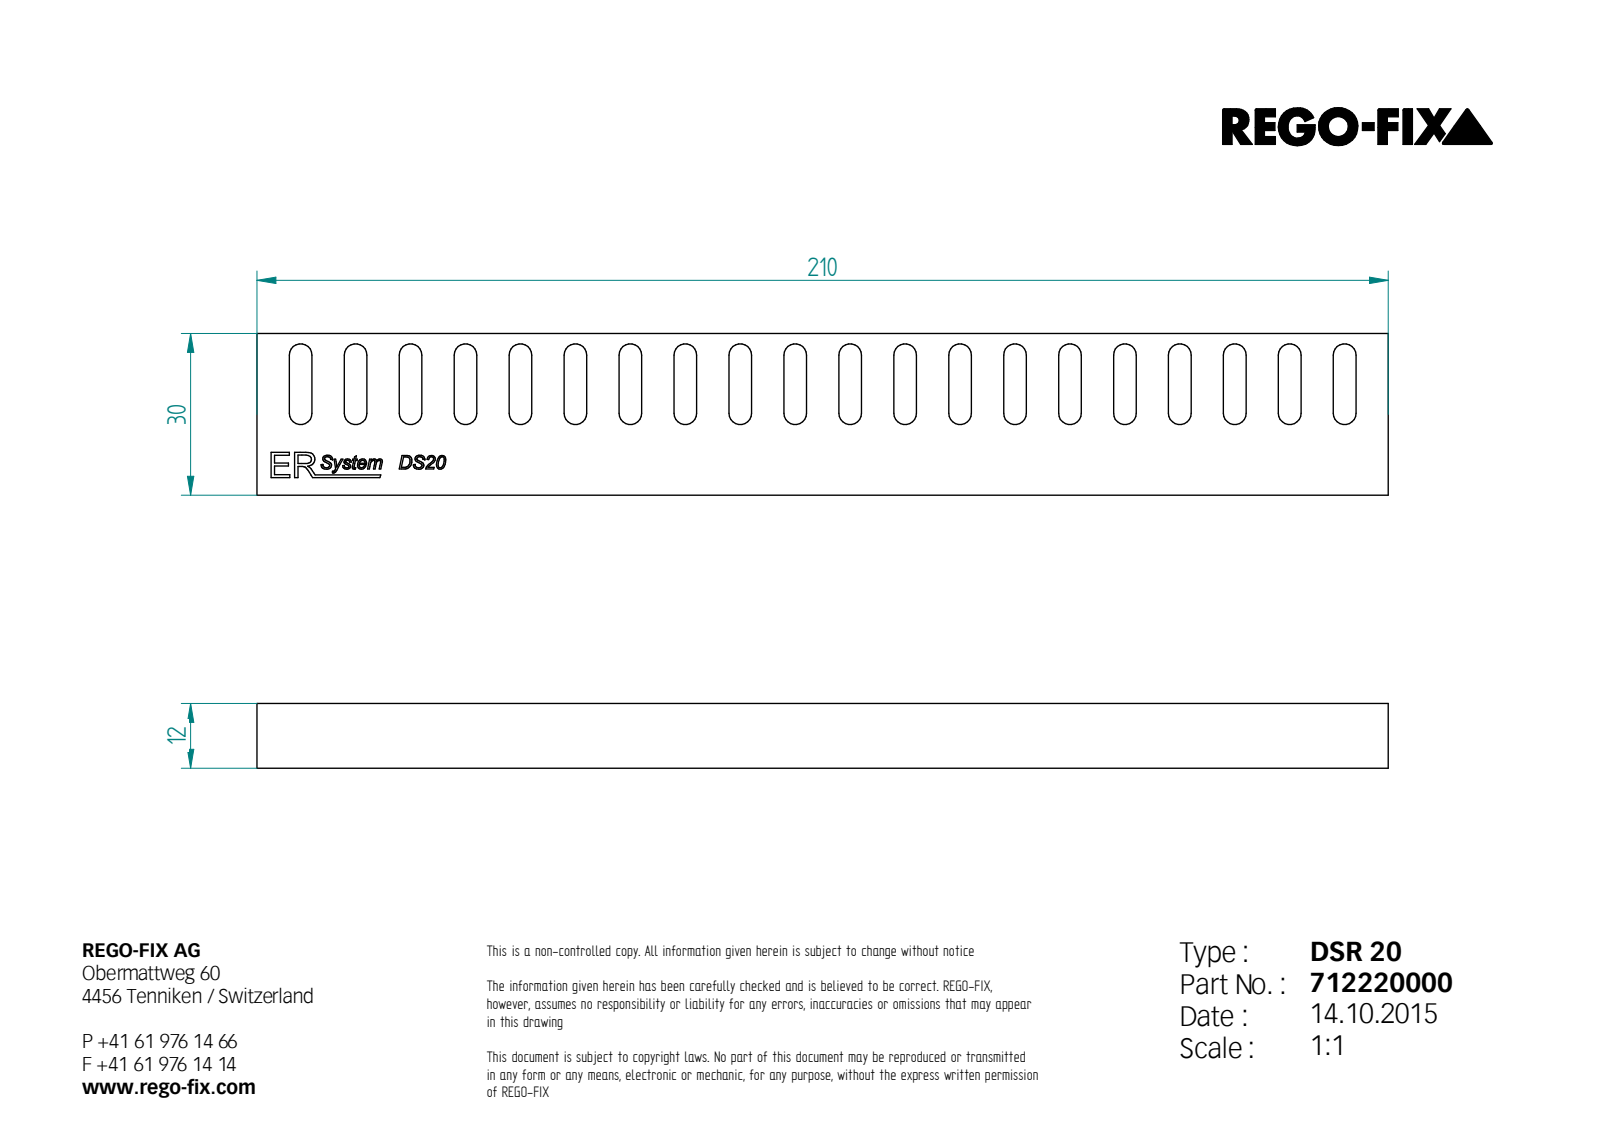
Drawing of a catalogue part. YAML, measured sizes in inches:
step_written_by: "Unknown (AUTOMOTIVE_DESIGN)"
units: inches
bodies: {solids: 1, faces: 205, planar: 137, cylindrical: 40, other: 28}
overall_size: [8.268, 1.181, 0.472]
volume: 4.179
surface_area: 34.99
partial_cylinders:
  - {radius: 0.083, count: 40}
face_to_face_distances: [0.472, 0.236, 1.181, 0.402, 0.803, 1.205, 0.165, 1.606, 0.638, 0.567]
